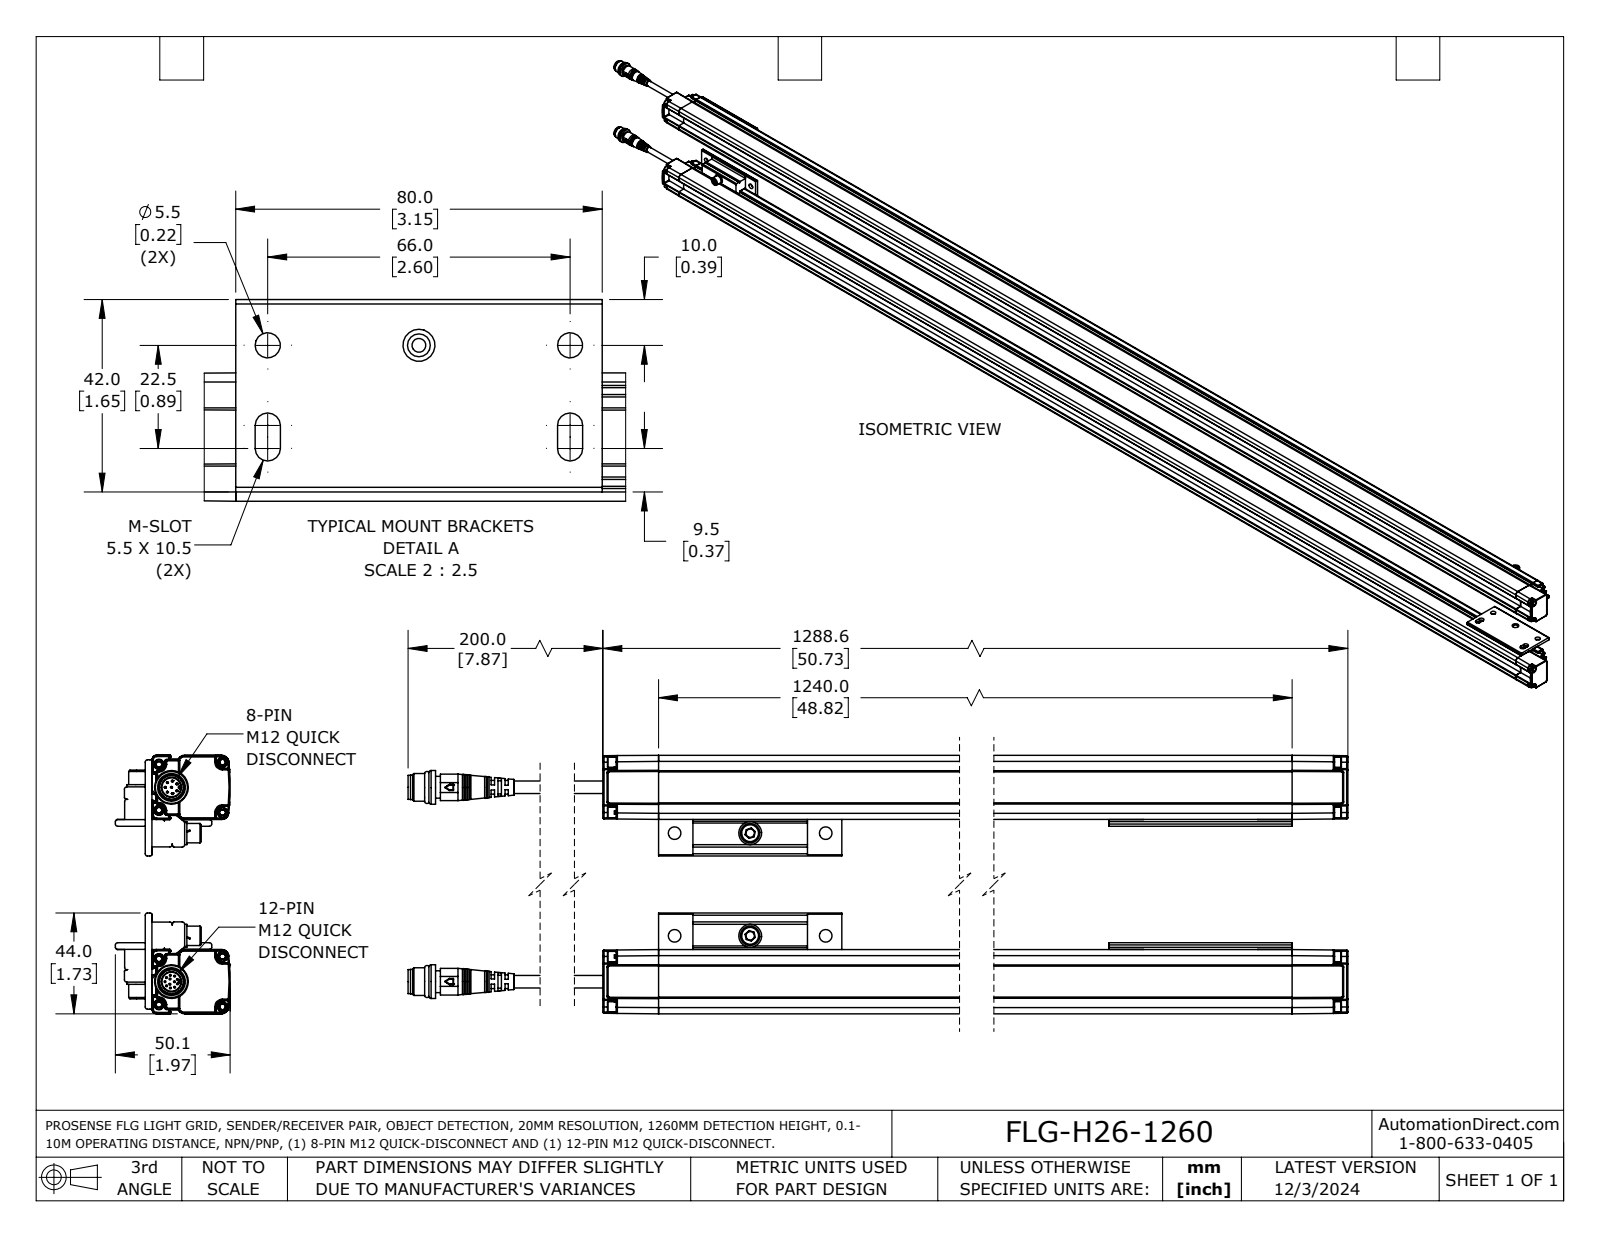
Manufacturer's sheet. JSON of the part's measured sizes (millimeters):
{"part_name": "FLG-H26-1260", "step_written_by": "SolidWorks 2023 (AUTOMOTIVE_DESIGN)", "units": "millimeters", "bodies": {"solids": 5, "faces": 869, "planar": 435, "cylindrical": 238, "other": 196}, "overall_size": [1380.5, 50.1, 44], "volume_mm3": 1036000, "surface_area_mm2": 254300, "round_holes": [[0.4, 16], [5.5, 4], [2.5, 2], [5, 2], [8.3, 1]], "round_bosses_or_shafts": [[0.8, 8], [4.5, 4], [3, 4], [10, 2], [8.5, 2], [5.5, 2], [3.7, 2], [1.5, 2]], "partial_cylinders_radius": [[0.5, 76], [1, 20], [0.3, 10], [2.7, 8], [0.2, 6], [0.3, 6], [2.5, 4], [1.2, 2]], "face_to_face_distances": [28, 1.8, 20.8, 7.2, 24.6, 26.4, 5.5, 26.2, 18.9, 13.5], "hole_center_spacings": [2.7, 4.1, 33, 5.5, 2.3, 2.3, 2.3, 3]}
